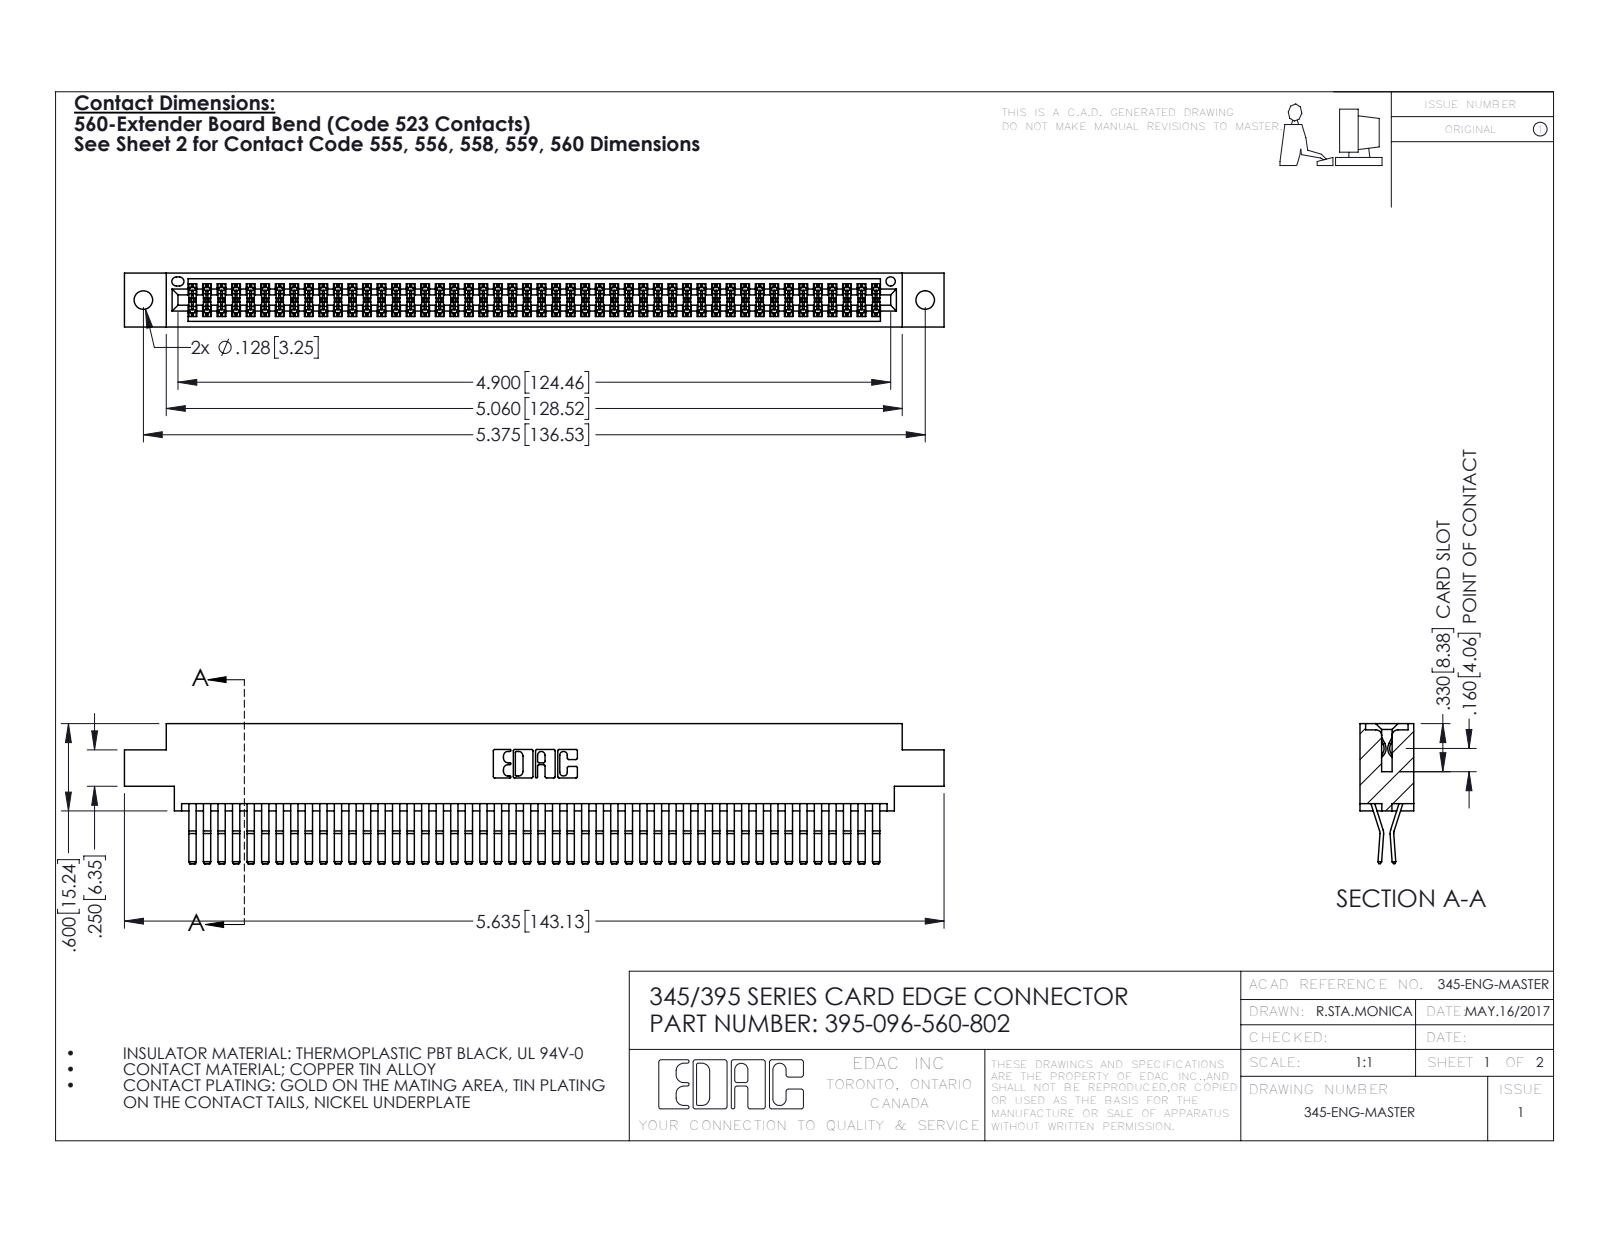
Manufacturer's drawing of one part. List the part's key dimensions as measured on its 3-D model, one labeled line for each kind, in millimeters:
Part name (STEP PRODUCT): 345-292-001_560 Tail; 345 Part_0.170 Offset - 0.128 Dia; 395-096-560-802
STEP written by: SolidWorks 2016 (CONFIG_CONTROL_DESIGN)
Units: millimetres
Bodies: 97 solids, 5122 faces (3252 planar, 1870 cylindrical, 0 other)
Overall size (bounding box): 143.1 × 24.4 × 9.4
Volume: 14 400 mm³ · Surface area: 22 950 mm²
Round holes (diameter × count): ⌀3.3 ×2, ⌀1.6 ×1
Partial cylindrical surfaces — rounded edges, fillets, slot ends (radius × count): R0.2 ×145, R0.3 ×22, R0.2 ×6, R0.8 ×6, R0.7 ×3, R0.3 ×2, R0.4 ×2, R0.5 ×2
Main face-to-face distances: 0.6, 7.6, 1.8, 9.4, 5.1, 2.5, 6.9, 5.7, 4.4, 3.8
Hole centre spacings: 6.9, 130.5, 136.5
